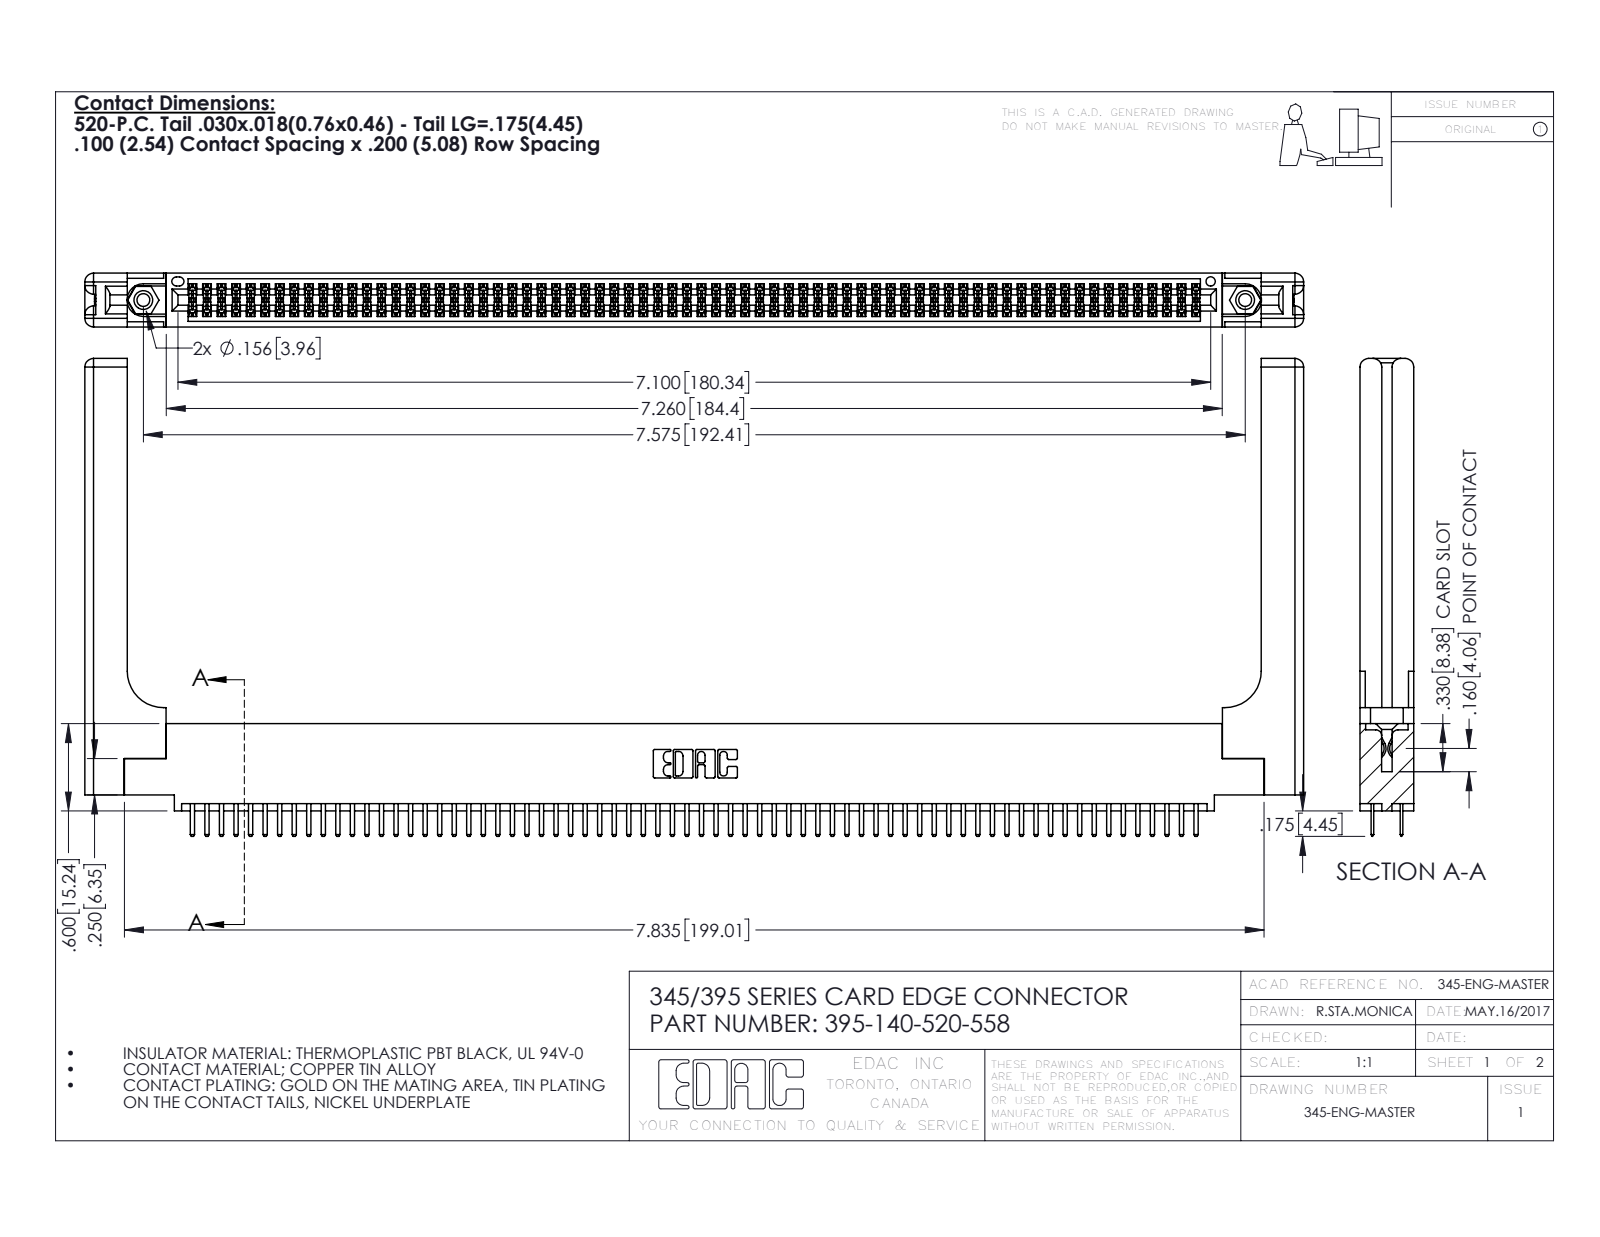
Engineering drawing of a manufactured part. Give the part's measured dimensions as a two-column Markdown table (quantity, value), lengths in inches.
| quantity | value |
| --- | --- |
| part name | 345-250-001_345-250-001-102; 345 Part_0.110 Offset - 0.156 Dia-TH; 395-140-520-558; 345-220-058_345-220-058 (+1 more) |
| STEP written by | SolidWorks 2016 (CONFIG_CONTROL_DESIGN) |
| units | inches |
| bodies | 145 solids, 7946 faces (5132 planar, 2754 cylindrical, 60 other) |
| overall size | 8.379 × 3.285 × 0.37 |
| volume | 1.786 in³ |
| surface area | 56.28 in² |
| round holes (diameter × count) | 0.089 × 2, 0.125 × 2, 0.156 × 2, 0.064 × 1 |
| round bosses / shafts (diameter × count) | 0.155 × 2 |
| partial cylindrical surfaces (radius × count) | 0.006 × 210, 0.01 × 144, 0.01 × 22, 0.06 × 16, 0.007 × 6, 0.031 × 6, 0.026 × 3, 0.014 × 2 |
| main face-to-face distances | 0.072, 0.298, 0.37, 0.2, 0.098, 0.272, 0.025, 0.225, 0.022, 0.072 |
| hole center spacings | 0.27, 7.339, 7.575 |
